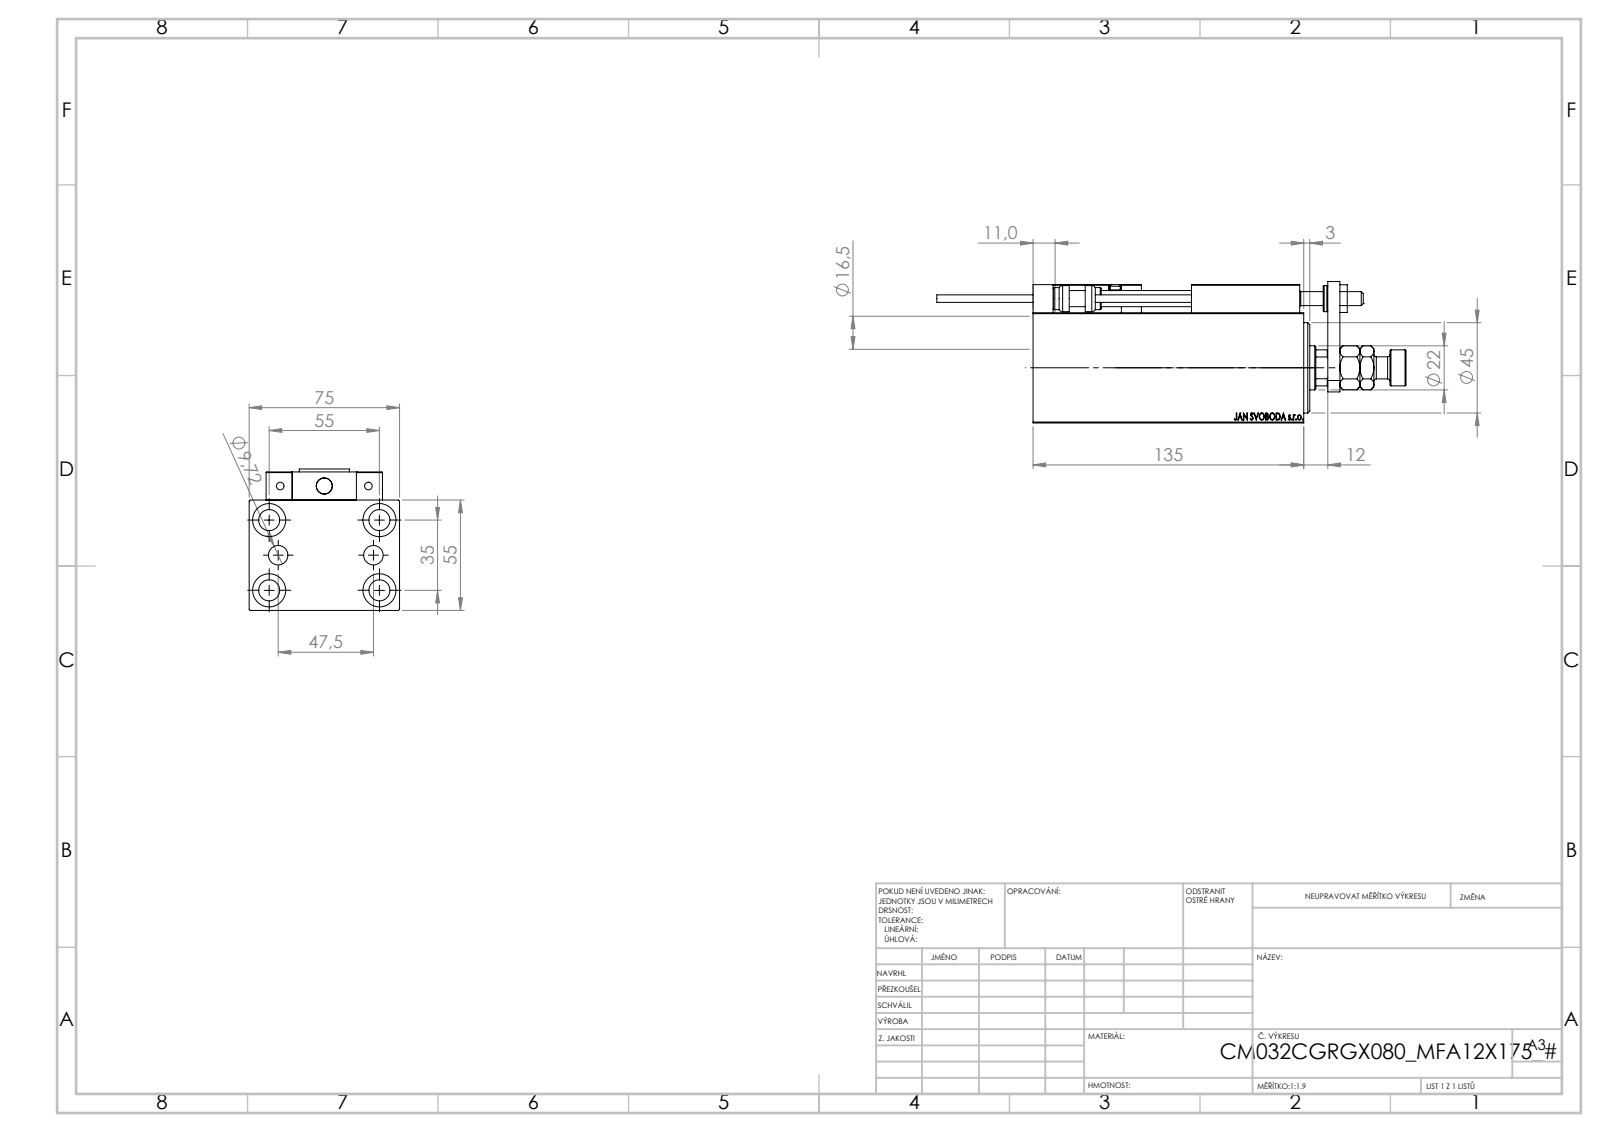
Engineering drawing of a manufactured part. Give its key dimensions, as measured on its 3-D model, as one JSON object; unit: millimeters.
{"part_name": "TYC_L79; V450CM_VC_B; SWITCH DIM B,W; ALLEN BOLT D5 (+8 more)", "step_written_by": "SolidWorks 2019 (CONFIG_CONTROL_DESIGN)", "units": "millimeters", "bodies": {"solids": 24, "faces": 1330, "planar": 576, "cylindrical": 188, "other": 566}, "overall_size": [234, 75, 70.5], "volume_mm3": 524820, "surface_area_mm2": 126605, "round_holes": [[4, 6], [8, 5], [10.5, 5], [16.5, 5], [3.2, 4], [5, 2], [9.72, 2], [7, 1], [22, 1], [25.5, 1], [32, 1], [34, 1]], "round_bosses_or_shafts": [[11, 2], [5, 2], [3.8, 2], [18, 1], [13, 1]], "partial_cylinders_radius": [[0.3, 30], [3, 2], [10.5, 1]], "face_to_face_distances": [55, 75, 14, 10, 69, 3, 25, 23, 18, 12], "hole_center_spacings": [17.9, 32.6, 54.16, 11.37, 20, 23.75, 29.59, 29.69]}
